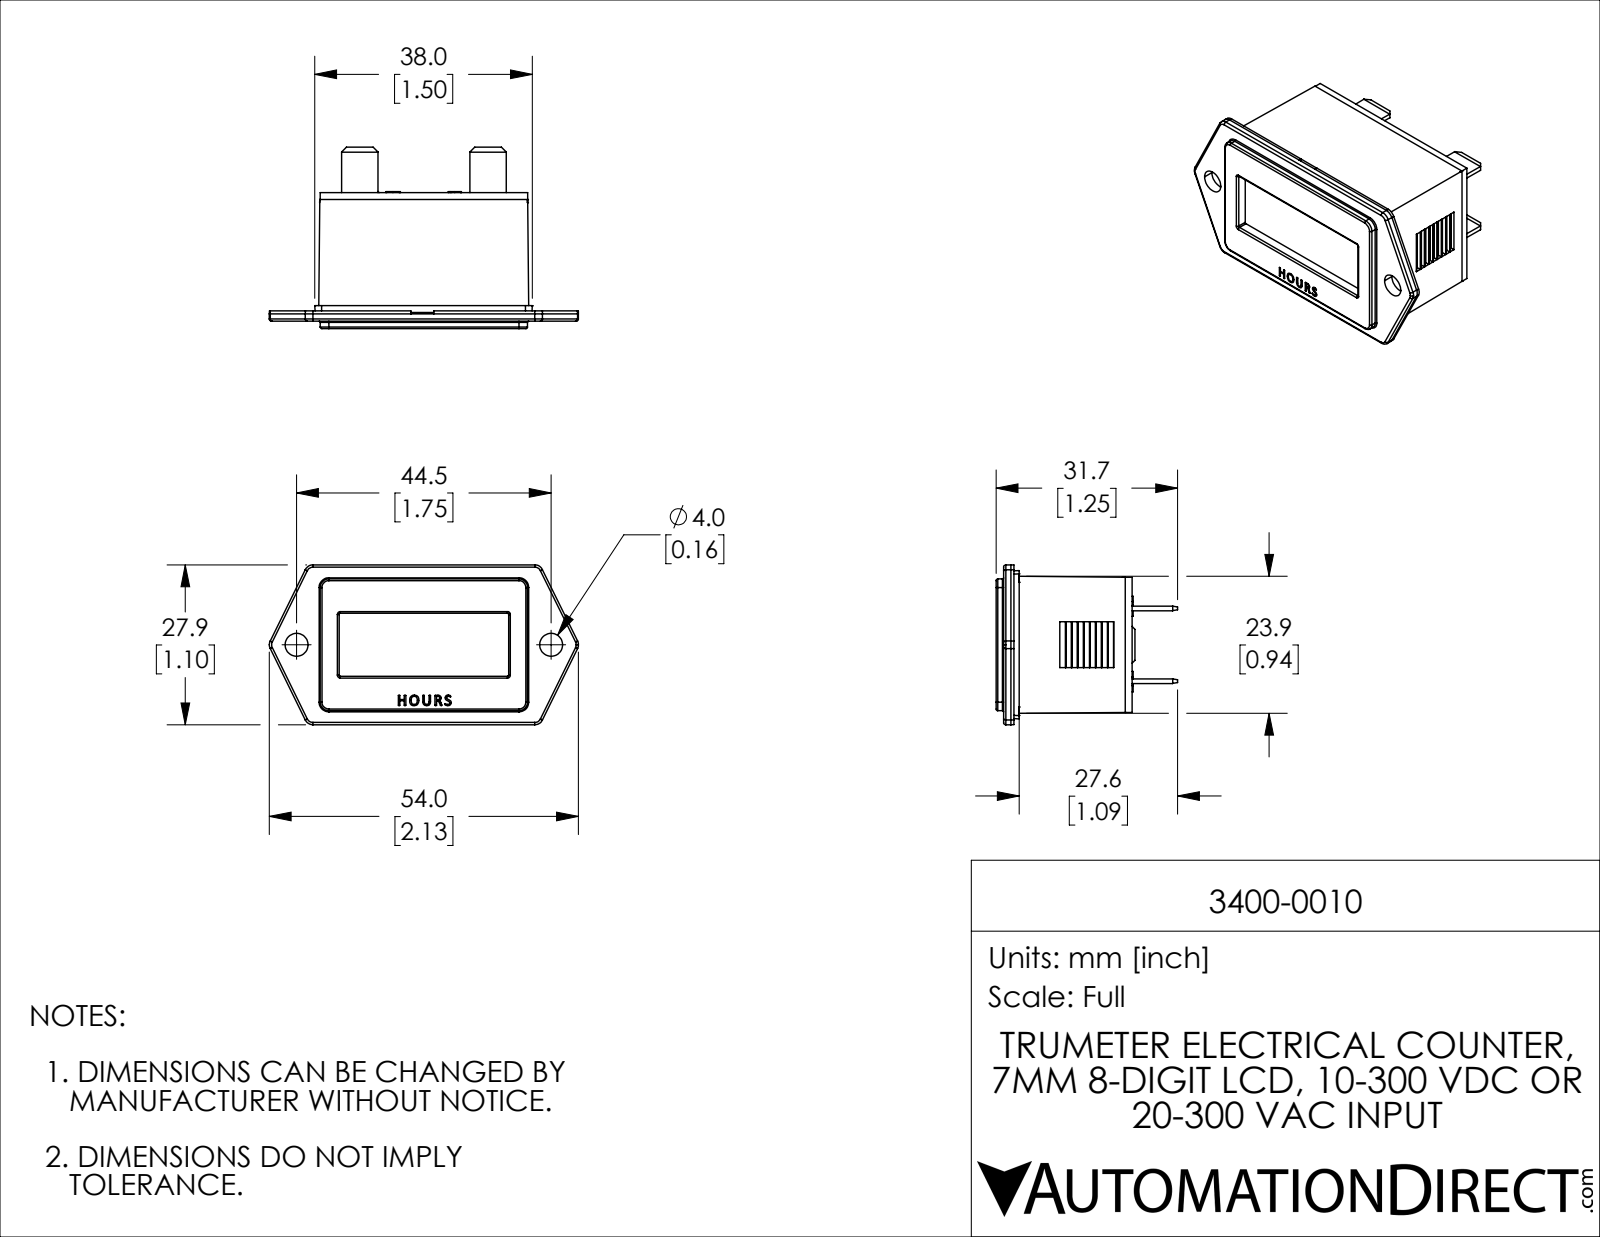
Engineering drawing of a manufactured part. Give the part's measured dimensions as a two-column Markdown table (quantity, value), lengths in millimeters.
| quantity | value |
| --- | --- |
| part name | 3400-0010 |
| STEP written by | SolidWorks 2021 (CONFIG_CONTROL_DESIGN) |
| units | millimeters |
| bodies | 2 solids, 618 faces (374 planar, 103 cylindrical, 141 other) |
| overall size | 53.98 × 31.68 × 27.9 |
| volume | 19 805 mm³ |
| surface area | 9 276 mm² |
| round holes (diameter × count) | 4 × 2 |
| partial cylindrical surfaces (radius × count) | 1.5 × 14, 0.2 × 8, 0.3 × 8, 0.25 × 6, 0.4 × 6, 0.76 × 4, 0.14 × 2, 0.25 × 2 |
| main face-to-face distances | 0.94, 20.9, 1.2, 21.84, 20.64, 20.61, 1.23, 19.67, 19.7, 0.8 |
| hole center spacings | 44.46 |
